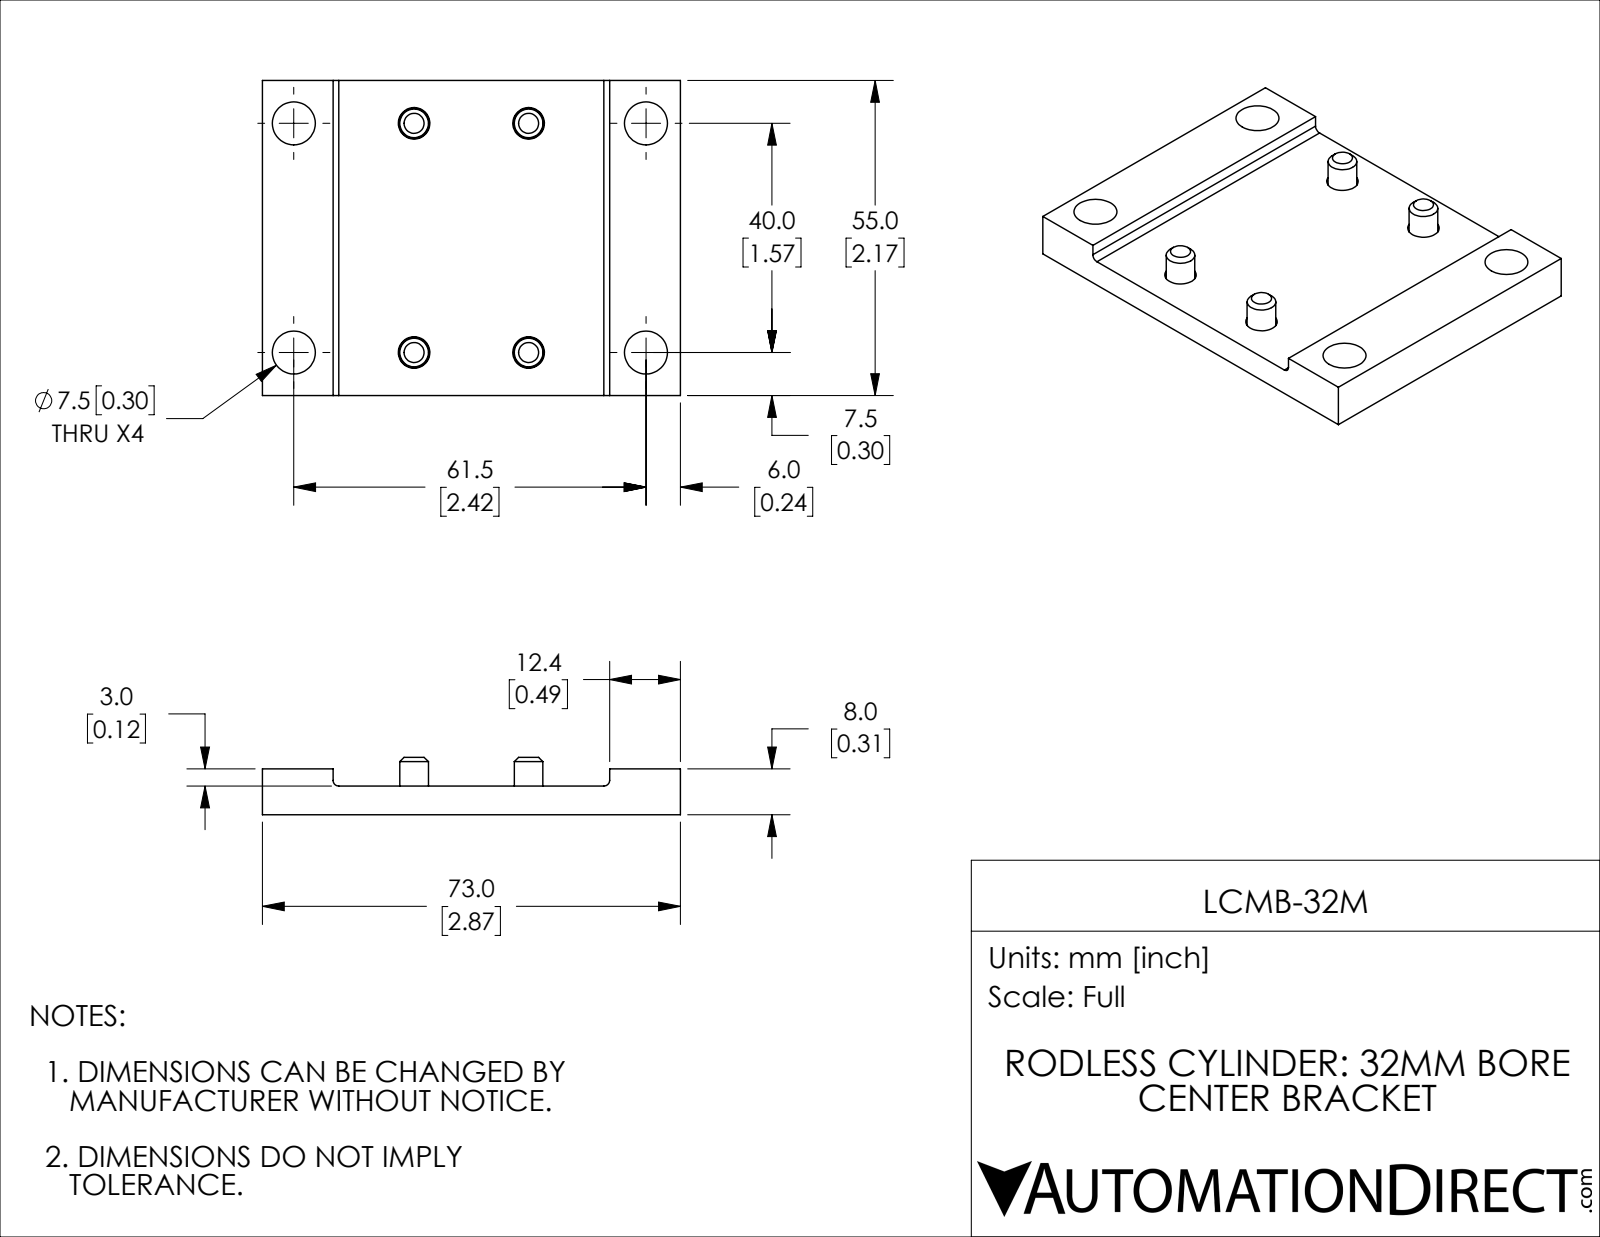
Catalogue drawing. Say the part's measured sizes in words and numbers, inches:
The part is named "LCMB-32M". Its 3-D file was written by "SolidWorks 2019 (CONFIG_CONTROL_DESIGN)". It is 5 solids with 184 faces: 102 planar, 42 cylindrical and 40 other. Overall it measures 2.874 by 2.165 by 0.394 inches. Its volume is 1.4 cubic inches and its surface area 18.28 square inches. Round holes: 4 of diameter 0.217, 4 of diameter 0.295. Round bosses or shafts: 4 of diameter 0.366, 4 of diameter 0.197, 4 of diameter 0.178. Partial cylindrical surfaces (rounded edges, fillets, slot ends): 2 of radius 0.039. The main face-to-face distances are 0.197, 0.315, 0.118, 2.874, 2.165, 0.486, 2.388, 1.902, 0.064, 0.133. The hole center spacings are 1.575, 0.787, 0.807, 0.827, 1.594, 1.614, 1.761, 1.77.
